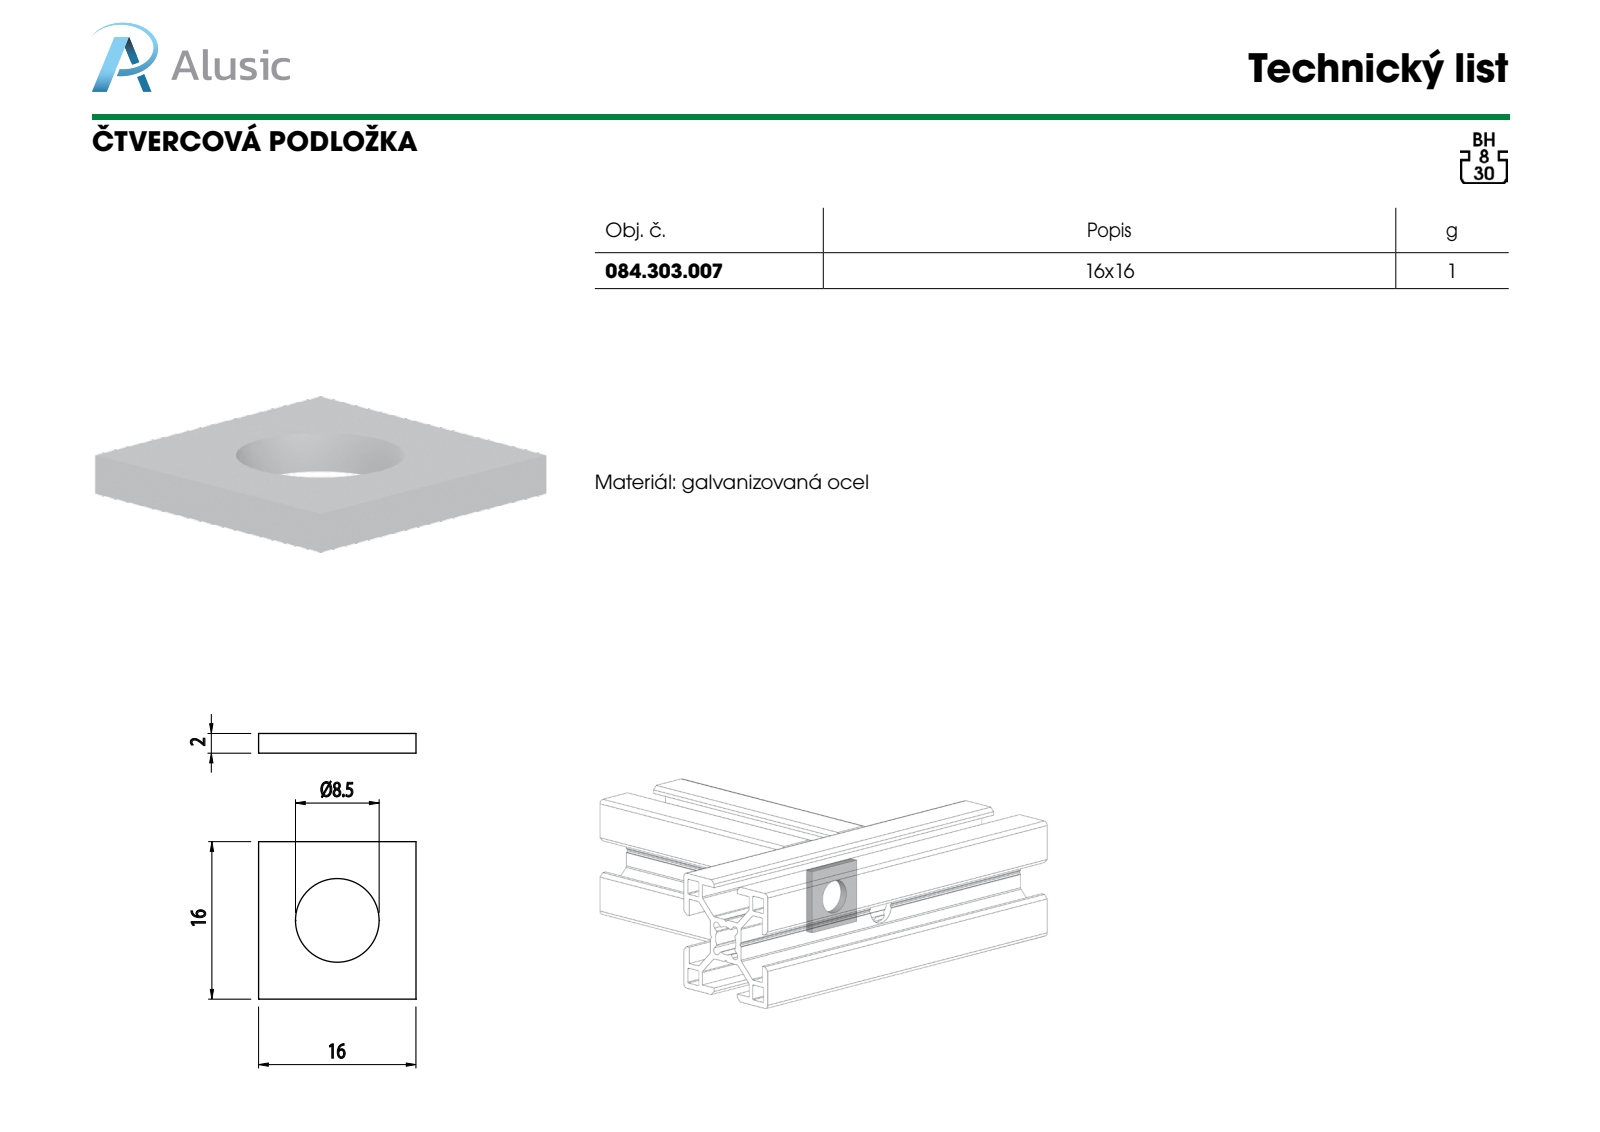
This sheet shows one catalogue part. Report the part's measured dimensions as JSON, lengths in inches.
{"part_name": "084.303.007", "step_written_by": "SolidWorks 2012 (CONFIG_CONTROL_DESIGN)", "units": "inches", "bodies": {"solids": 1, "faces": 8, "planar": 6, "cylindrical": 2, "other": 0}, "overall_size": [0.63, 0.63, 0.079], "volume_in3": 0.024, "surface_area_in2": 0.899, "round_holes": [[0.335, 1]], "face_to_face_distances": [0.079, 0.63]}
